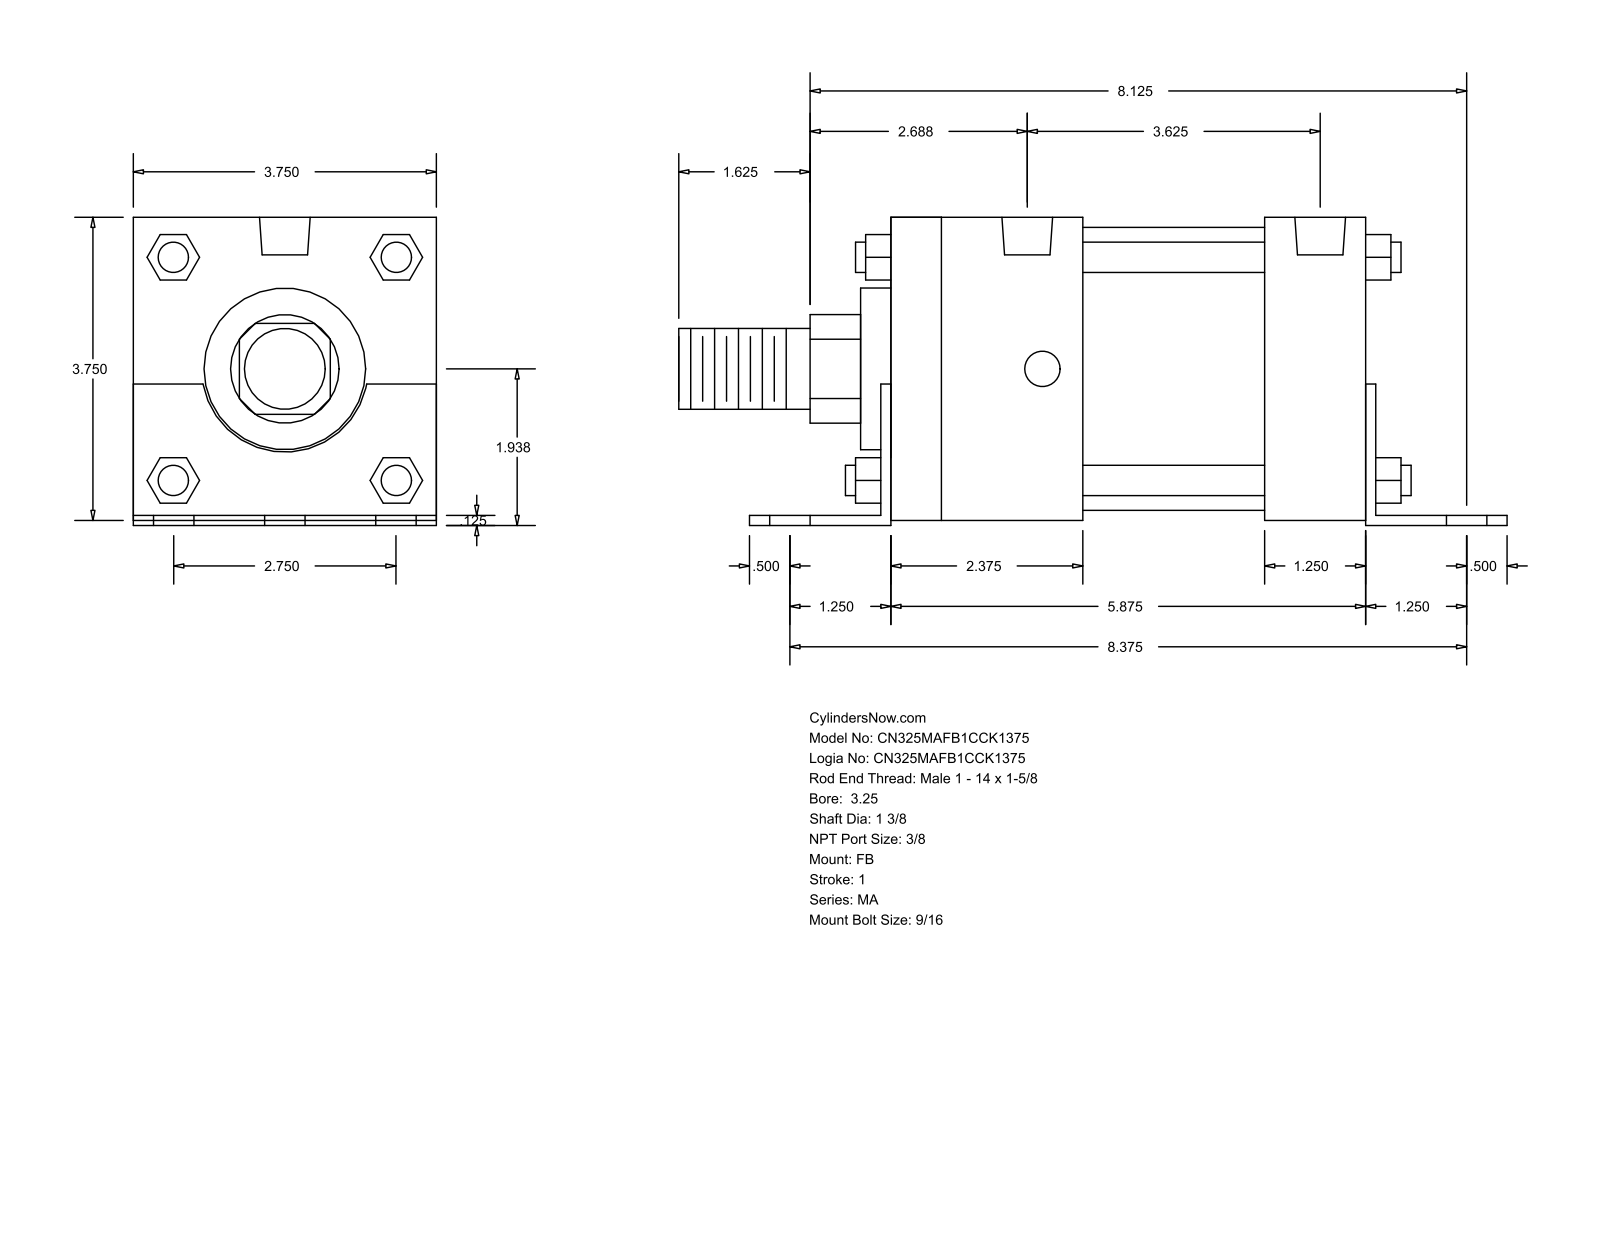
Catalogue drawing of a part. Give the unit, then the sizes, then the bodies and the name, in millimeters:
Units: millimetres
Overall size (bounding box): 260.35 × 96.84 × 95.25
Round holes (diameter × count): ⌀14.29 ×6, ⌀11.11 ×4, ⌀15.93 ×2
Round bosses / shafts (diameter × count): ⌀9.53 ×4, ⌀88.9 ×1, ⌀50.8 ×1, ⌀34.92 ×1, ⌀25.4 ×1
Partial cylindrical surfaces — rounded edges, fillets, slot ends (radius × count): R17.06 ×1, R26.16 ×1
Main face-to-face distances: 95.24, 3.17, 1.59, 96.83, 1.58, 93.66, 3.18, 149.22, 152.4, 34.92
Hole centre spacings: 34.92, 215.58, 212.73, 4.77, 57.78, 61.65, 69.84, 82.38
Bodies: 0 solids, 140 faces (105 planar, 35 cylindrical, 0 other)
Part name (STEP PRODUCT): MA_FB__0325_1.375
STEP written by: GSSL Pune (CONFIG_CONTROL_DESIGN)
